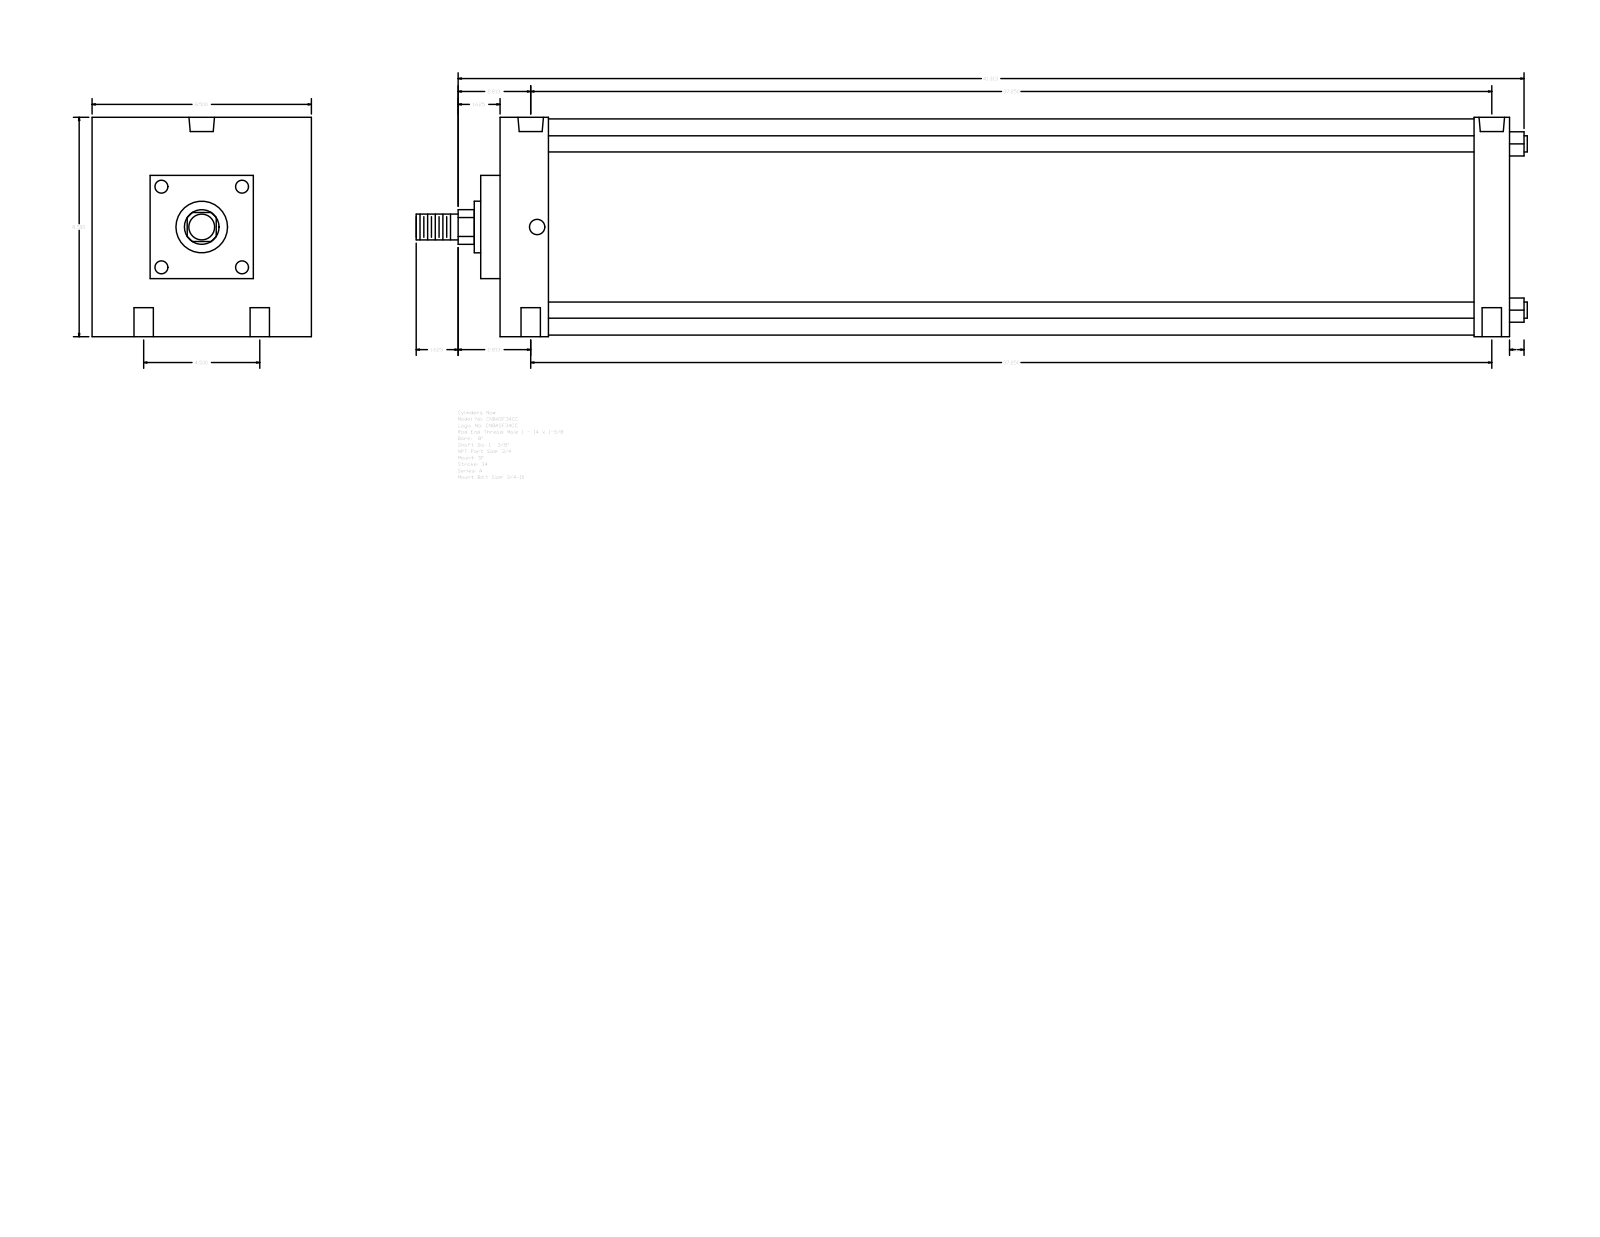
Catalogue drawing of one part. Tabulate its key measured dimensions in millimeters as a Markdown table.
| quantity | value |
| --- | --- |
| part name | A_SF__0800_1.375 |
| STEP written by | GSSL Pune (CONFIG_CONTROL_DESIGN) |
| units | millimeters |
| bodies | 0 solids, 93 faces (67 planar, 26 cylindrical, 0 other) |
| overall size | 1093.79 × 215.9 × 215.9 |
| round holes (diameter × count) | 19.05 × 4, 15.08 × 2, 25.12 × 2 |
| round bosses / shafts (diameter × count) | 15.88 × 4, 212.72 × 1, 50.8 × 1, 34.92 × 1, 25.4 × 1 |
| partial cylindrical surfaces (radius × count) | 17.06 × 1 |
| main face-to-face distances | 993.78, 215.9, 47.63, 958.85, 911.22, 946.15, 34.93, 19.04, 66.67, 977.89 |
| hole center spacings | 57.15, 947.87, 946.15, 114.3, 953.03, 933.45 |
